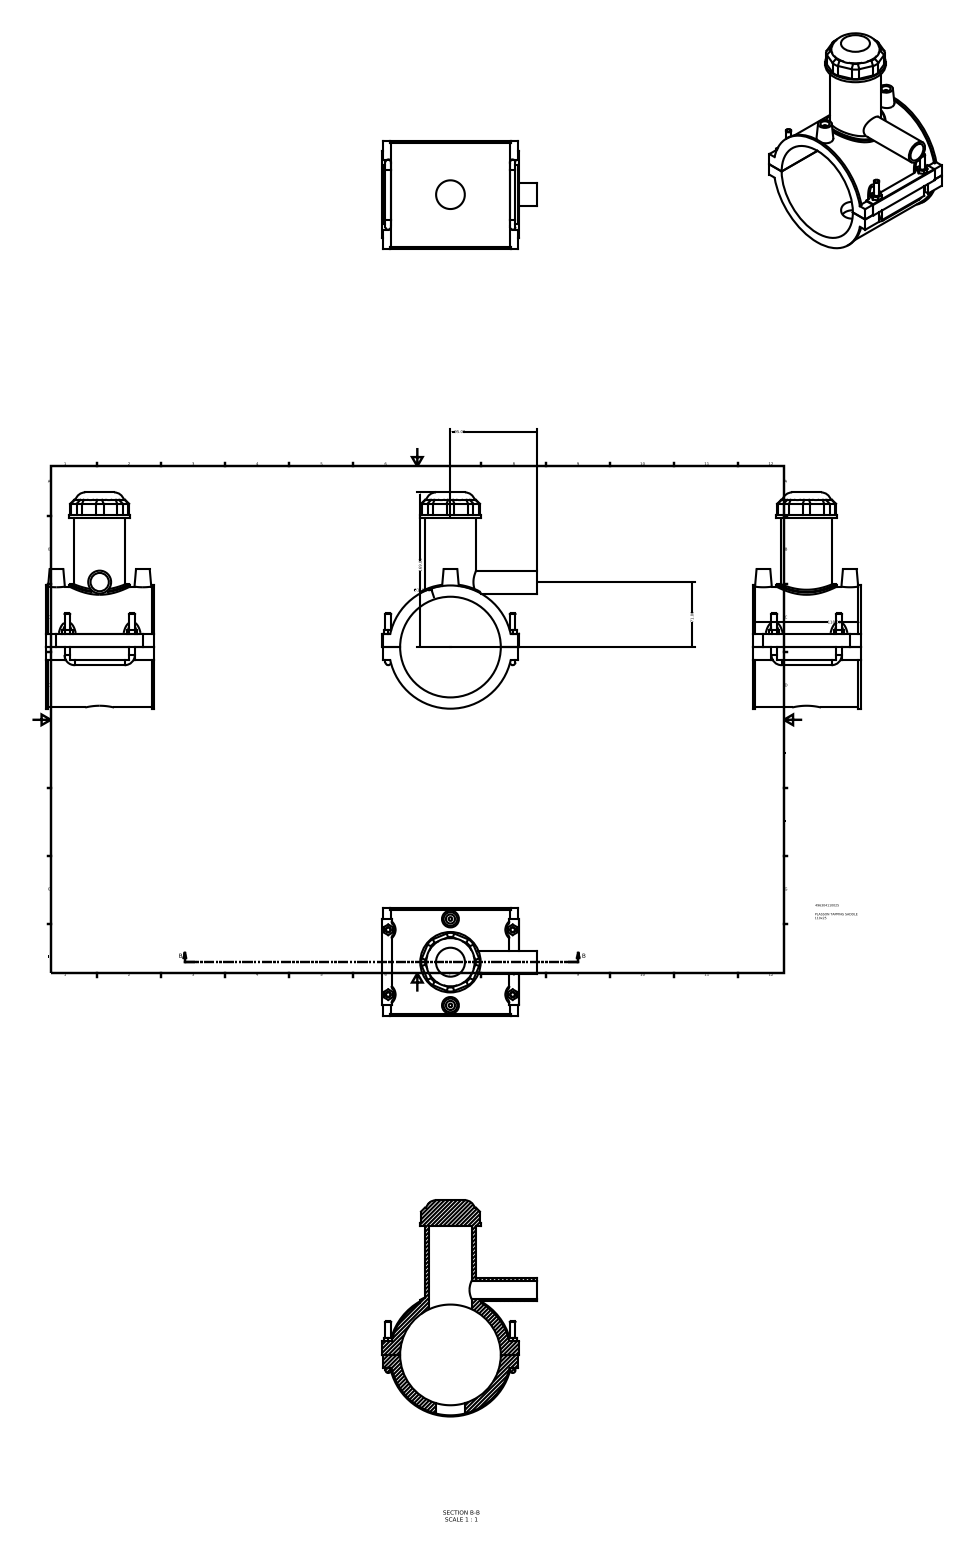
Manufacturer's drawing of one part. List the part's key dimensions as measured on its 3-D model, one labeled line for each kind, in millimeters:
Part name (STEP PRODUCT): 496304110025
STEP written by: Autodesk Inventor 2015 (AUTOMOTIVE_DESIGN)
Units: millimetres
Bodies: 1 solid, 188 faces (117 planar, 47 cylindrical, 24 other)
Overall size (bounding box): 236.32 × 170 × 118
Volume: 689 817 mm³ · Surface area: 164 592 mm²
Round holes (diameter × count): ⌀10 ×2, ⌀20 ×1, ⌀31.36 ×1, ⌀46.2 ×1, ⌀110 ×1
Round bosses / shafts (diameter × count): ⌀6 ×6, ⌀4 ×2, ⌀134.64 ×1, ⌀132 ×1, ⌀66 ×1, ⌀56.1 ×1, ⌀25 ×1
Partial cylindrical surfaces — rounded edges, fillets, slot ends (radius × count): R11 ×8, R3 ×4, R7.5 ×4, R0.5 ×1, R68.64 ×1
Main face-to-face distances: 118, 1, 154.25, 149, 140.55, 140.45, 28.5, 13.7, 13.8, 14.8
Hole centre spacings: 47.2, 94.4
